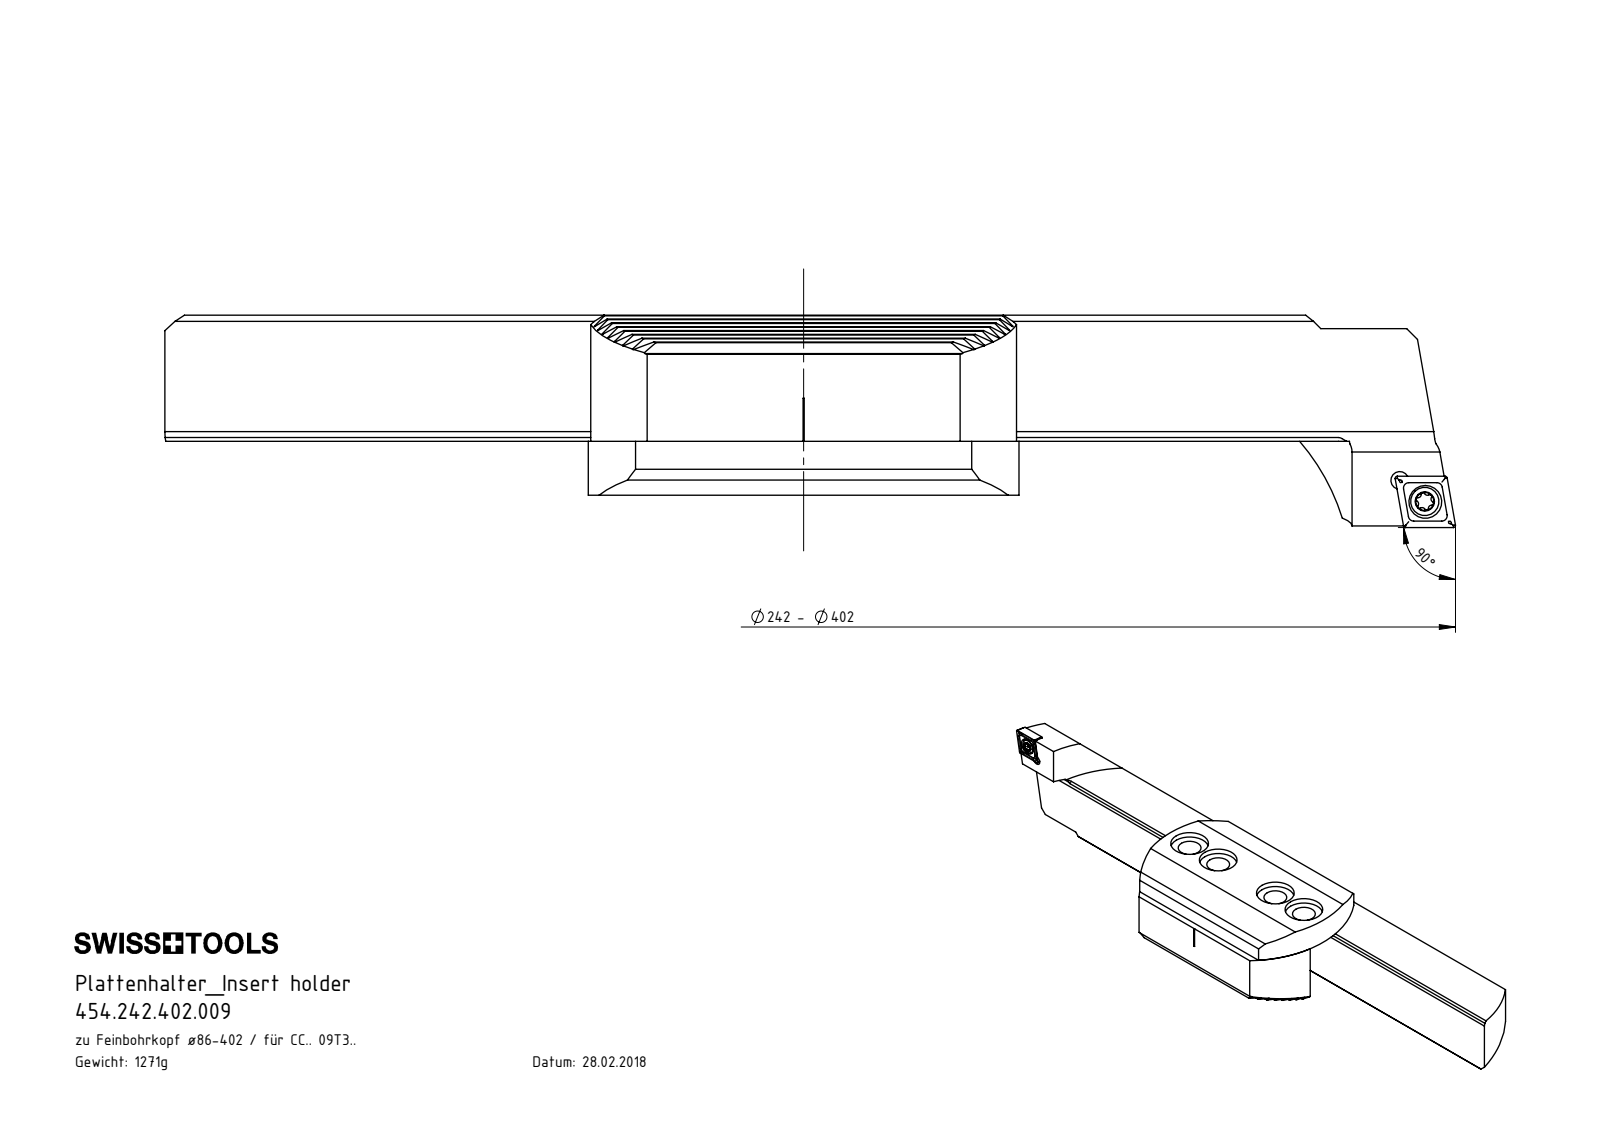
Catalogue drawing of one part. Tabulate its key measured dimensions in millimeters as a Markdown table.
| quantity | value |
| --- | --- |
| part name | 454.242.402.009; F00-WCB.136.002_A; F00-WCB.136.003_A; F00-WCB.242.001 (+3 more) |
| STEP written by | SolidWorks 2017 (CONFIG_CONTROL_DESIGN) |
| units | millimeters |
| bodies | 5 solids, 992 faces (604 planar, 67 cylindrical, 321 other) |
| overall size | 239.57 × 55 × 39.4 |
| volume | 161 949 mm³ |
| surface area | 41 929 mm² |
| round holes (diameter × count) | 8.5 × 4, 14 × 4, 3.3 × 2, 4.4 × 1, 6.1 × 1 |
| round bosses / shafts (diameter × count) | 5.25 × 1, 4 × 1 |
| partial cylindrical surfaces (radius × count) | 0.2 × 16, 0.34 × 6, 0.59 × 6, 40 × 6, 0.8 × 1 |
| main face-to-face distances | 2.38, 4.76, 21.3, 7.14, 33.7, 9.52, 4.77, 7.15, 9.53, 11.91 |
| hole center spacings | 15, 45, 6.06, 6.19, 30, 60 |
